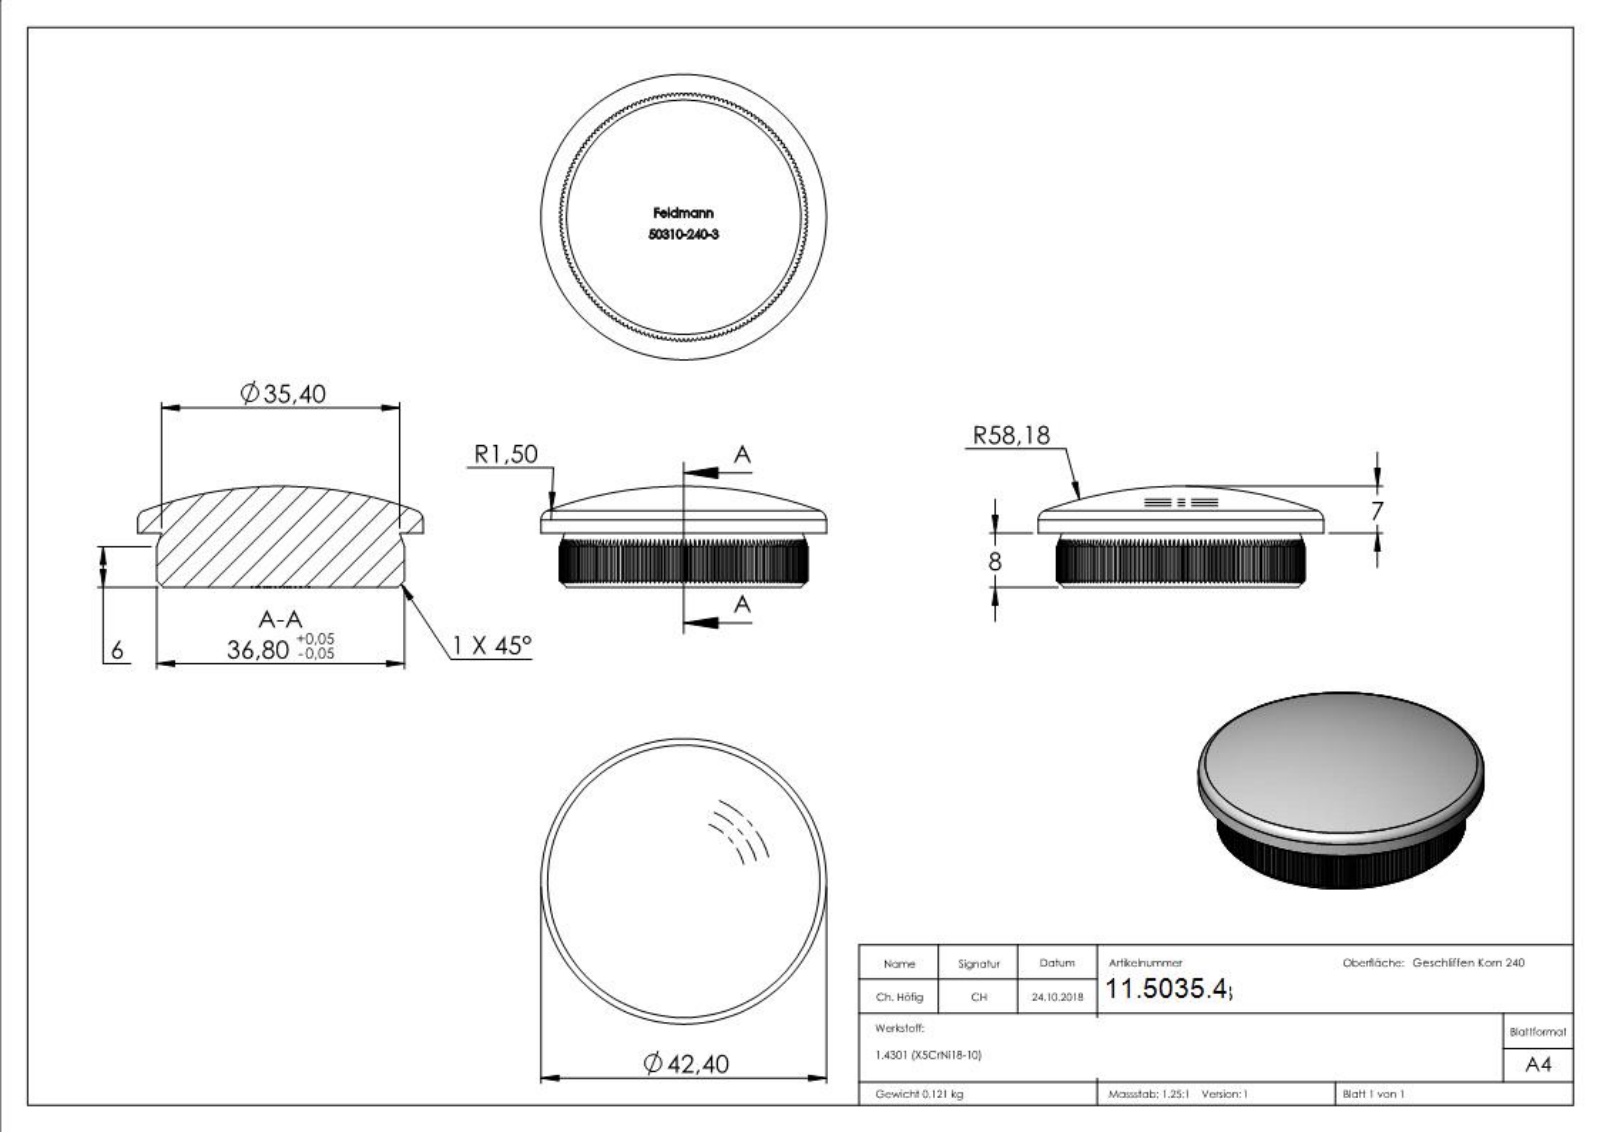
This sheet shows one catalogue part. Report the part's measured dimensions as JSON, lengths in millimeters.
{"part_name": "50310-240-3", "step_written_by": "SolidWorks 2015 (CONFIG_CONTROL_DESIGN)", "units": "millimeters", "bodies": {"solids": 1, "faces": 744, "planar": 461, "cylindrical": 172, "other": 111}, "overall_size": [42.4, 42.4, 15], "volume_mm3": 15374, "surface_area_mm2": 4574, "round_bosses_or_shafts": [[42.4, 1]], "partial_cylinders_radius": [[18.4, 1]], "face_to_face_distances": [8, 18.06, 18.04, 18.08, 7.9, 2.97, 0.39, 1.4, 3.39, 3.19]}
